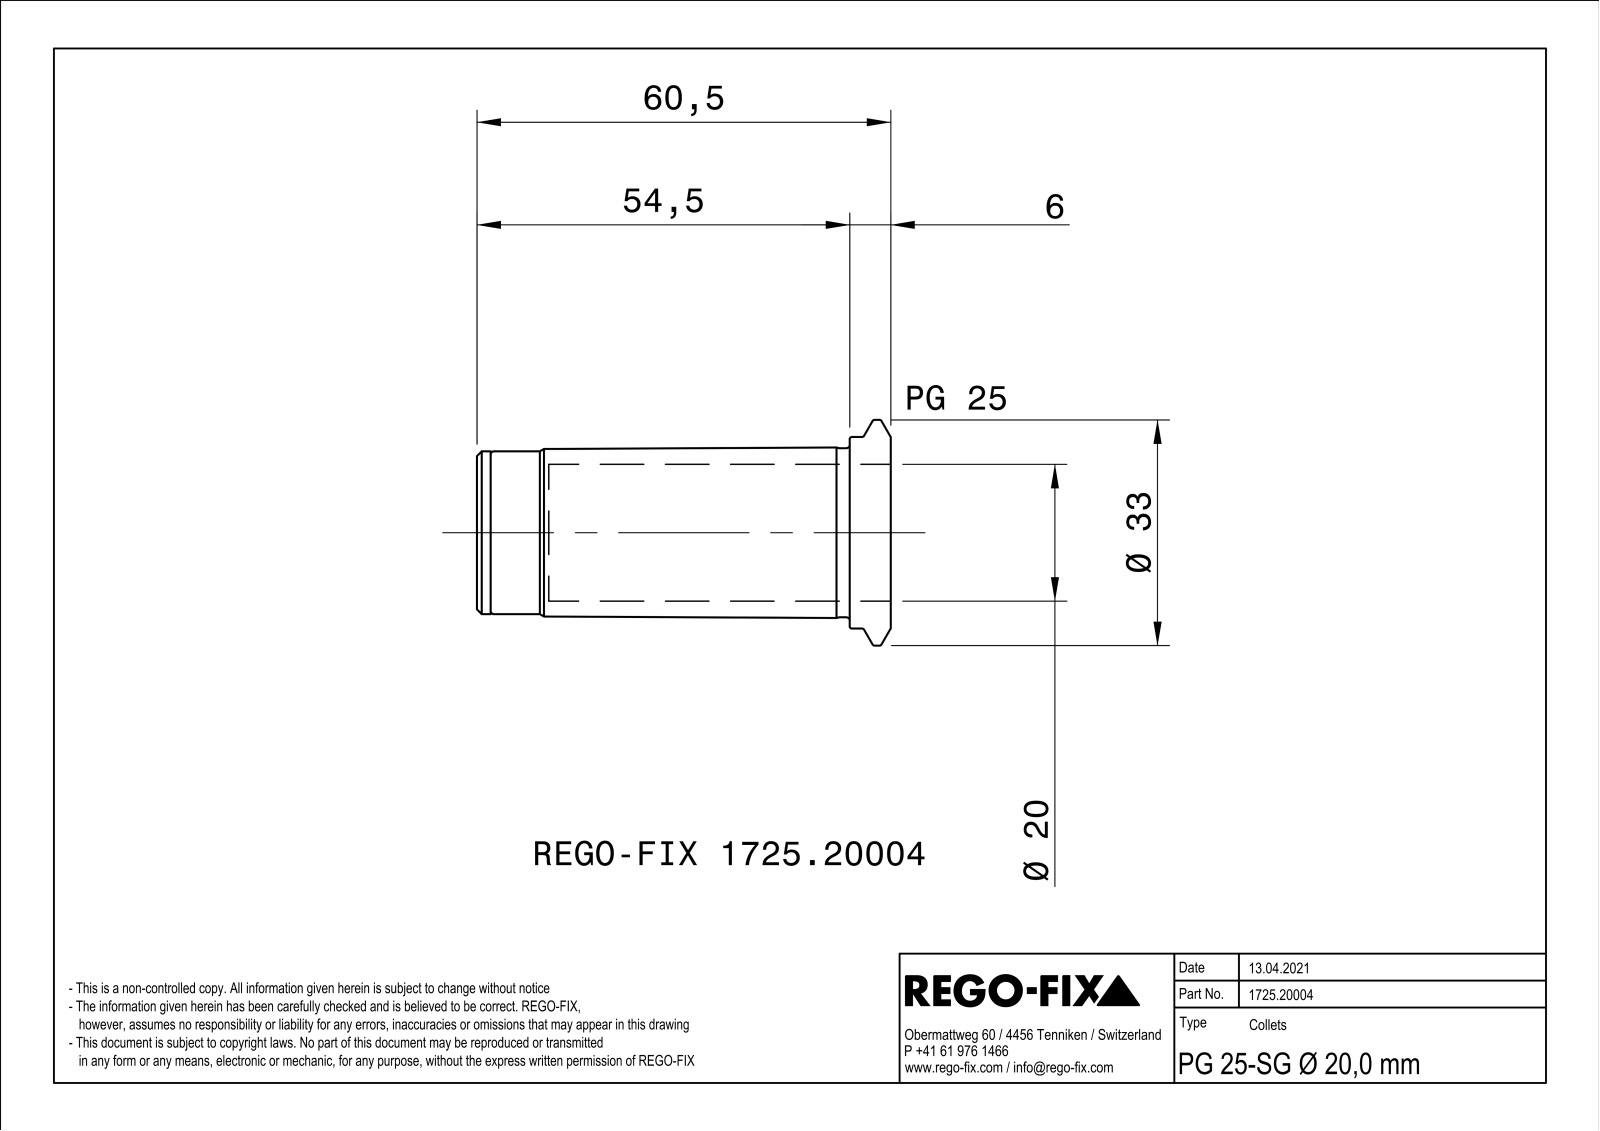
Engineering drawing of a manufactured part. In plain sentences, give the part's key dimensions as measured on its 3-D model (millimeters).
The part is named "NOCUT". Its 3-D file was written by "SIEMENS PLM Software Solid Edge ST10 (AUTOMOTIVE_DESIGN)". It is 1 solid with 85 faces: 23 planar, 23 cylindrical and 39 other. Overall it measures 60.5 by 33 by 32.99 millimeters. Round holes: 3 of diameter 2.5, 1 of diameter 5.2, 1 of diameter 6.92, 1 of diameter 8.2, 1 of diameter 20, 1 of diameter 20.4, 1 of diameter 20.92, 1 of diameter 22.2. Round bosses or shafts: 1 of diameter 33, 1 of diameter 28, 1 of diameter 24.7, 1 of diameter 23.8, 1 of diameter 12. The main face-to-face distances are 1, 60.5, 52.6, 7.9, 58.5, 5.9, 2, 50, 2.6, 8.5. The hole center spacings are 7.75, 13.43, 13.42.
